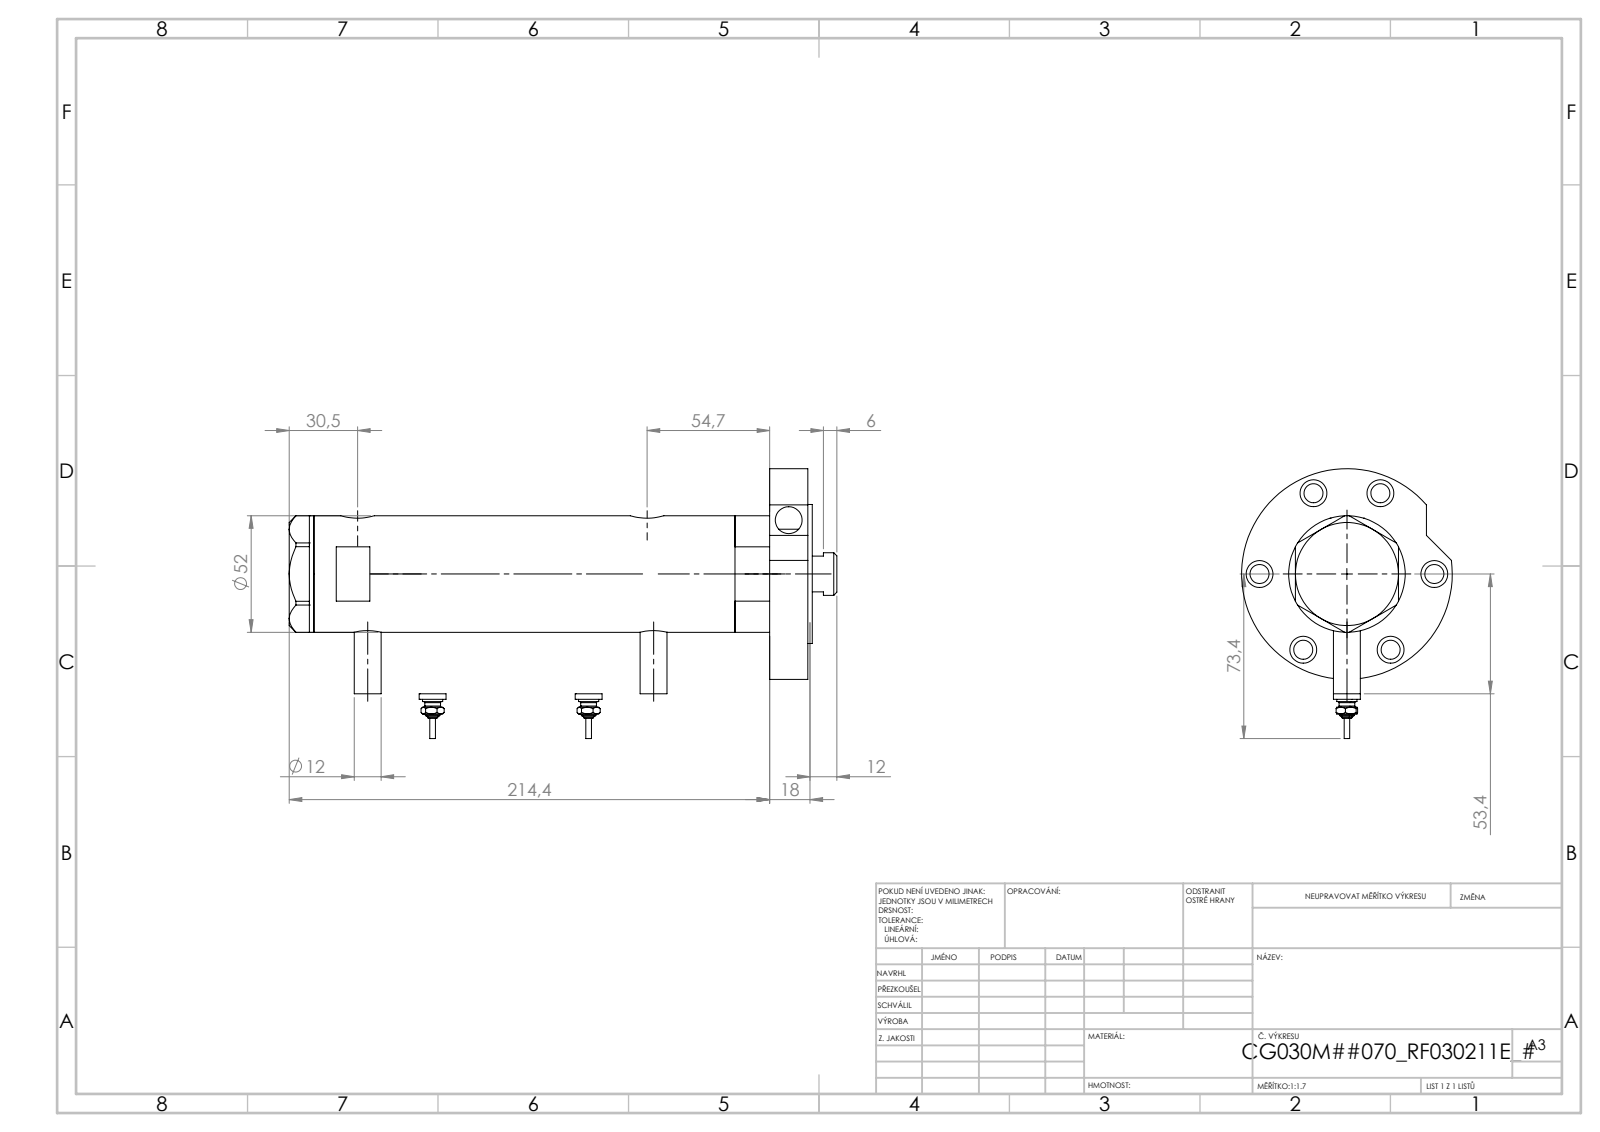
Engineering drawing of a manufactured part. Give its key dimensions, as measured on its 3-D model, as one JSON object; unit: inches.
{"part_name": "V270CG_SWITCH; V270CG_MIDDLE; V270CG_FRONT; V270CG_RF211E (+2 more)", "step_written_by": "SolidWorks 2019 (CONFIG_CONTROL_DESIGN)", "units": "inches", "bodies": {"solids": 7, "faces": 290, "planar": 106, "cylindrical": 110, "other": 74}, "overall_size": [8.623, 4.146, 3.701], "volume_in3": 28.89, "surface_area_in2": 175.5, "round_holes": [[0.472, 7], [0.335, 6], [0.197, 2], [0.383, 2], [0.492, 2], [0.591, 2], [0.256, 1], [0.787, 1], [0.846, 1], [1.181, 1], [1.299, 1], [1.575, 1]], "round_bosses_or_shafts": [[0.472, 3], [0.354, 2], [0.276, 2], [0.171, 2], [0.094, 2], [3.701, 1], [2.441, 1], [2.047, 1]], "face_to_face_distances": [0.669, 6.907, 7.576, 2.043, 0.079, 7.655, 4.864, 2.713, 2.791, 0.748], "hole_center_spacings": [1.535, 0.114, 0.177, 1.706, 2.553, 2.659, 2.754, 3.064]}
